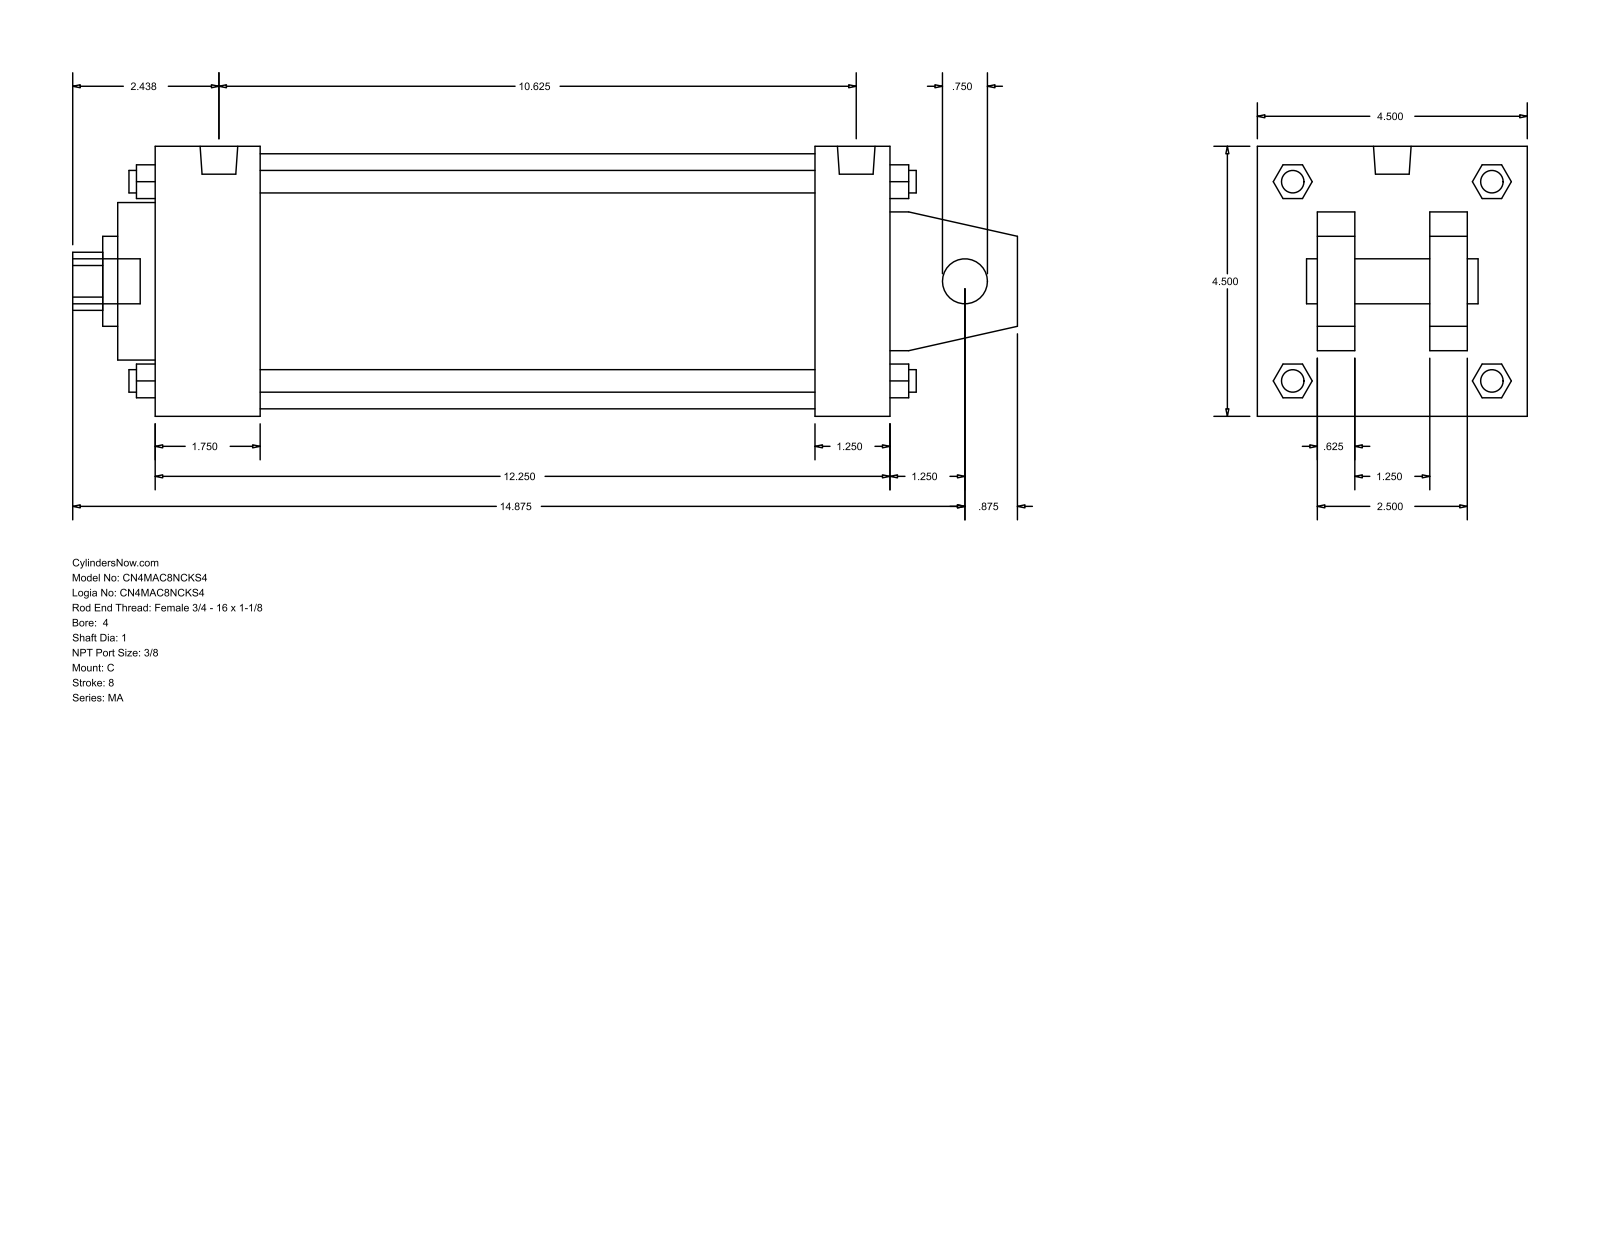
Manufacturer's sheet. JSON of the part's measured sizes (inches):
{"part_name": "MA_C__0400_1", "step_written_by": "GSSL Pune (CONFIG_CONTROL_DESIGN)", "units": "inches", "bodies": {"solids": 0, "faces": 141, "planar": 109, "cylindrical": 32, "other": 0}, "overall_size": [15.75, 4.5, 4.5], "round_holes": [[0.75, 1], [1, 1], [1.5, 1], [2.625, 1], [4.25, 1]], "round_bosses_or_shafts": [[0.437, 4], [0.375, 4], [0.627, 2], [0.75, 1]], "partial_cylinders_radius": [[0.484, 1]], "face_to_face_distances": [4.5, 12.25, 0.625, 2.875, 1.625, 1, 3.5, 1.875, 11, 1.25]}
